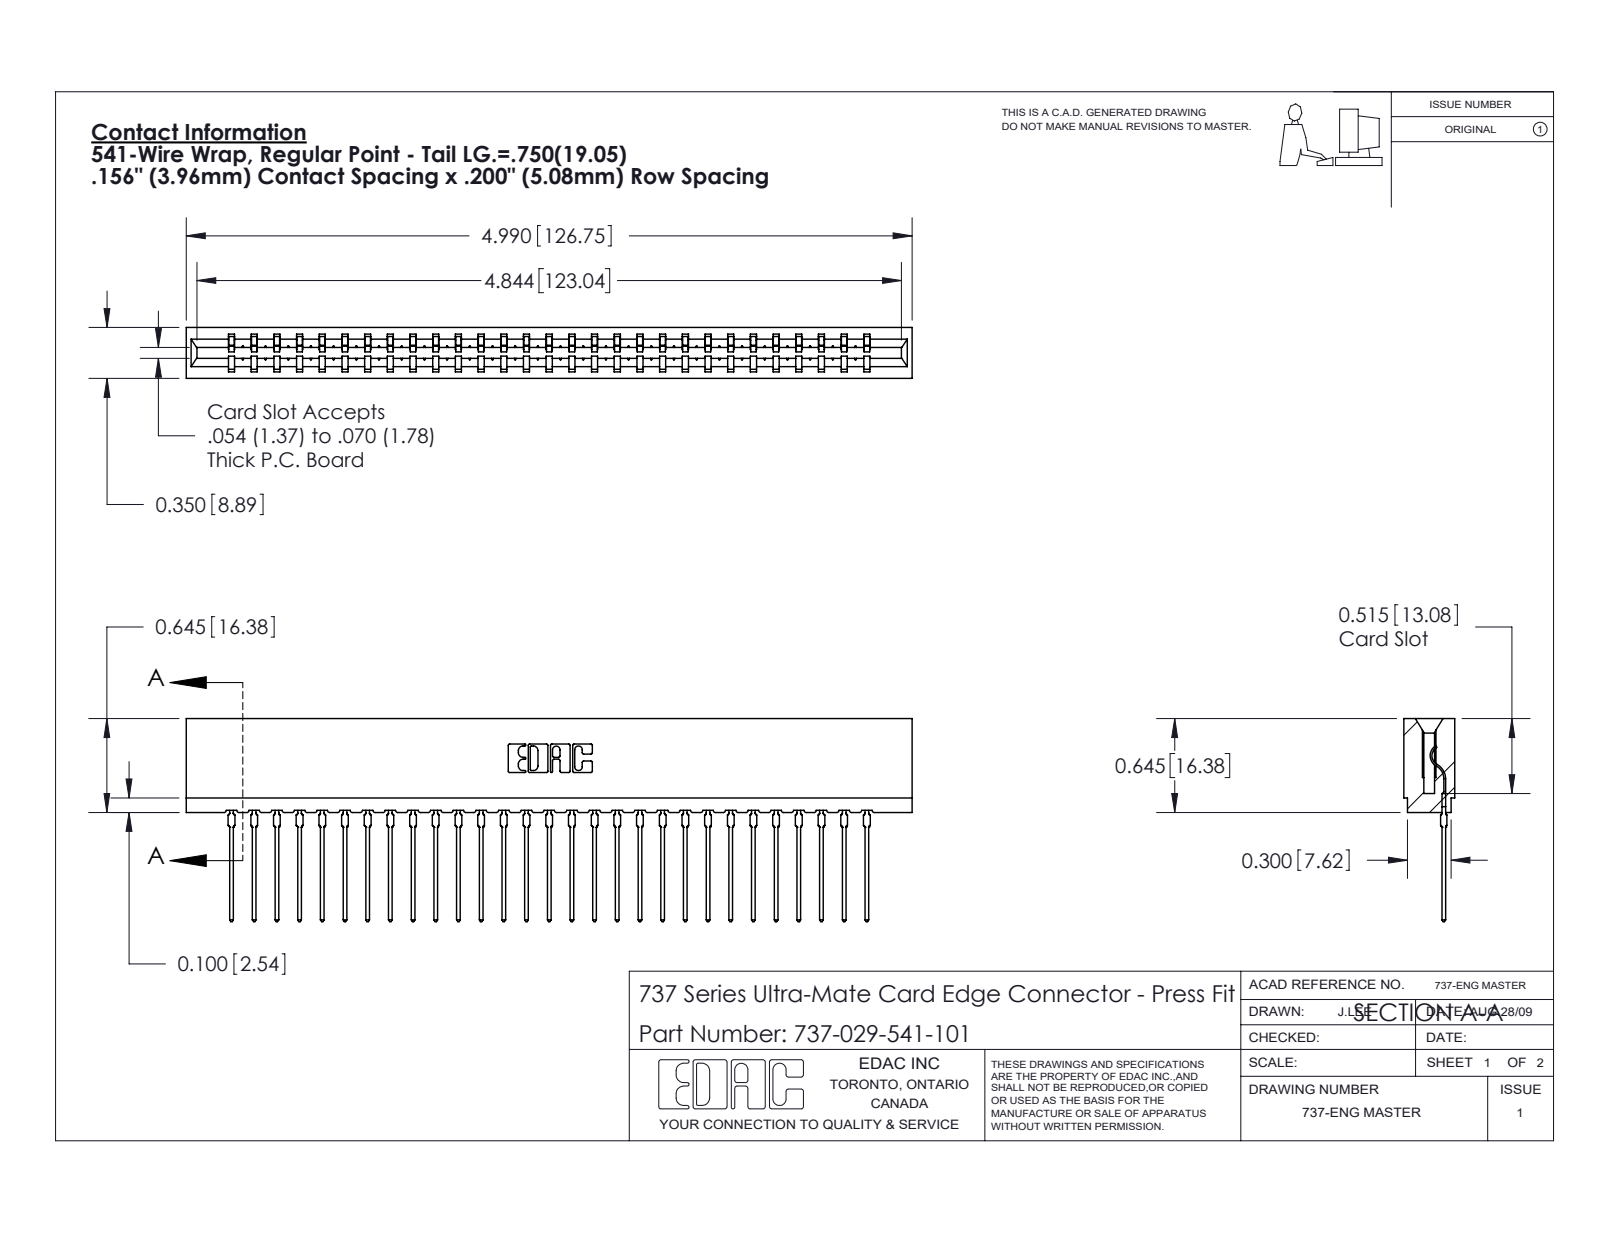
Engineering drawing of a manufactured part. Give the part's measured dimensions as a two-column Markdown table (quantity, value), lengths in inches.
| quantity | value |
| --- | --- |
| part name | 737-029-541-101; 745-292-001_541; 737 Part_Insulator Option - 01 |
| STEP written by | SolidWorks 2020 (CONFIG_CONTROL_DESIGN) |
| units | inches |
| bodies | 30 solids, 3371 faces (2026 planar, 591 cylindrical, 754 other) |
| overall size | 4.99 × 1.396 × 0.35 |
| volume | 0.761 in³ |
| surface area | 26.57 in² |
| partial cylindrical surfaces (radius × count) | 0.015 × 58, 0.021 × 58, 0.01 × 22, 0.007 × 6, 0.031 × 6, 0.005 × 4, 0.011 × 4, 0.026 × 3 |
| main face-to-face distances | 0.138, 0.212, 0.35, 0.074, 0.063, 0.287, 0.076, 0.149, 0.045, 0.305 |
